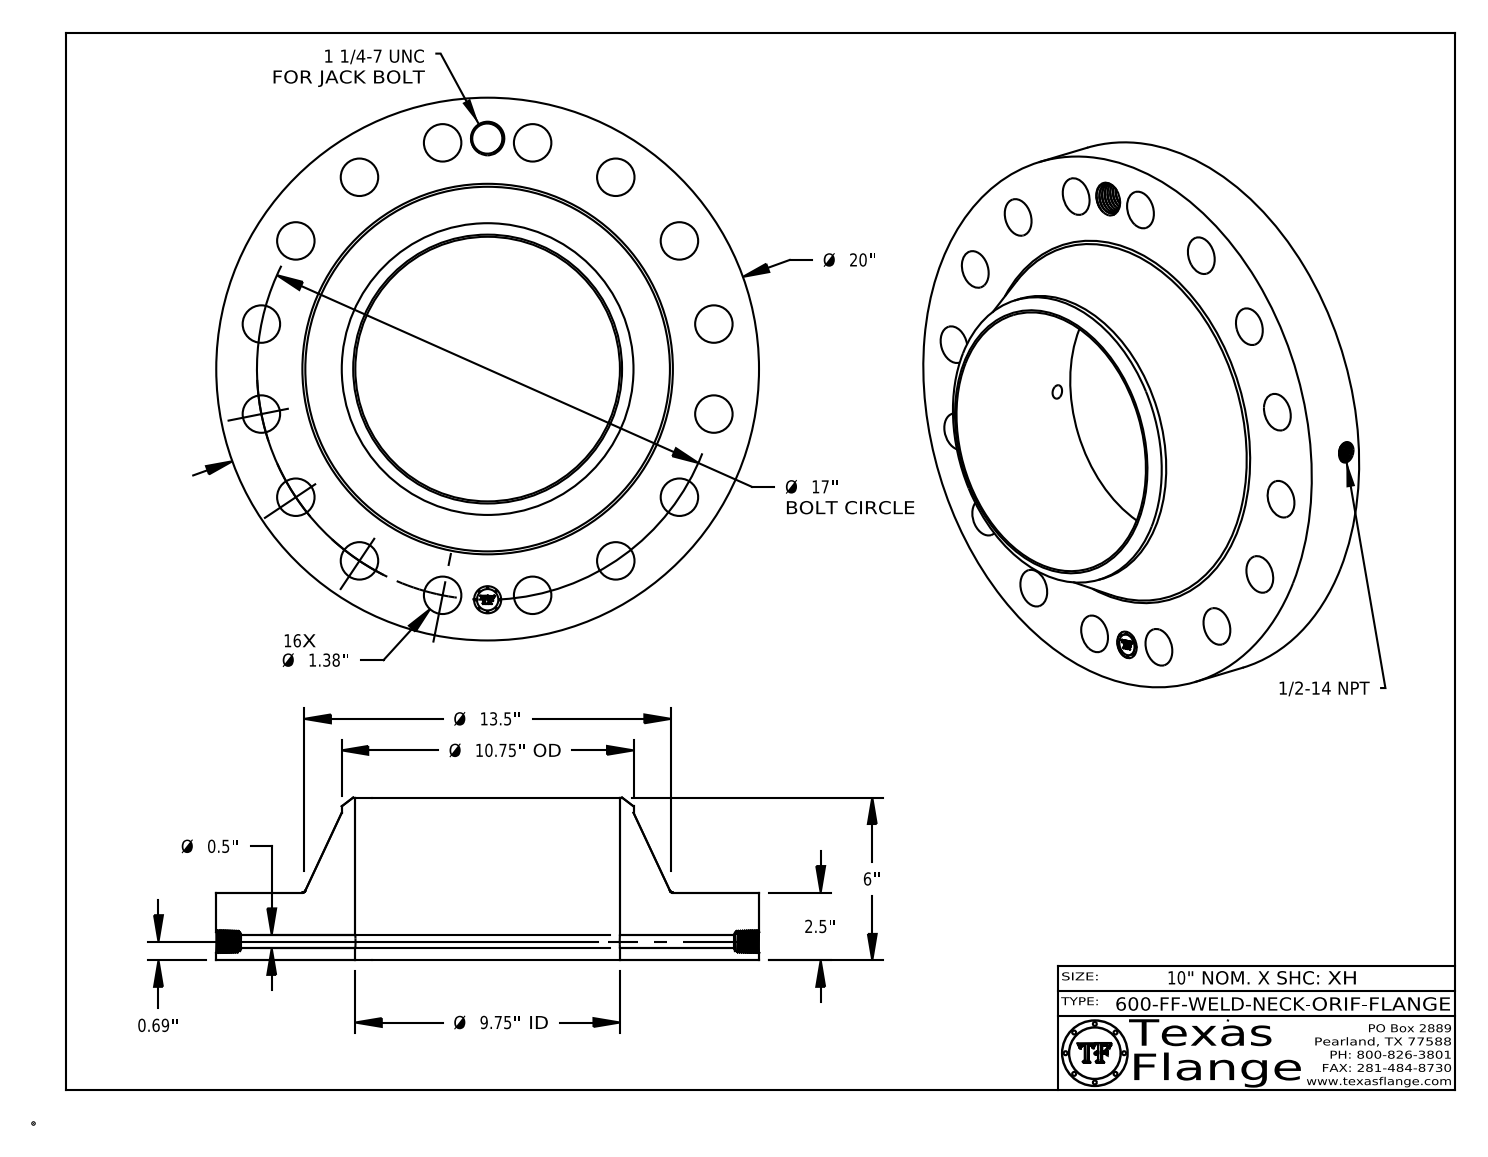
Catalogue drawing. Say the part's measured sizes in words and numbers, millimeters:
The part is named "600-FF-WELD-NECK". Its 3-D file was written by "CATIA V5 STEP AP214 (AUTOMOTIVE_DESIGN)". It is 1 solid with 799 faces: 368 planar, 113 cylindrical and 318 other. Overall it measures 508 by 508 by 152.4 millimeters. Its volume is 10 850 000 cubic millimeters and its surface area 682 600 square millimeters. Round holes: 16 of diameter 35.1, 1 of diameter 12.7, 1 of diameter 17.1, 1 of diameter 25.4, 1 of diameter 28.2, 1 of diameter 247.7. Round bosses or shafts: 8 of diameter 1.5, 1 of diameter 508, 1 of diameter 273.1, 1 of diameter 20. The main face-to-face distances are 63.5, 152.4, 88.9, 63.1, 0.4, 89.3, 7.6, 7.4, 1.4, 6.3. The hole center spacings are 215.9, 305.3, 398.9, 423.5, 84.3, 239.9, 359, 431.8.
